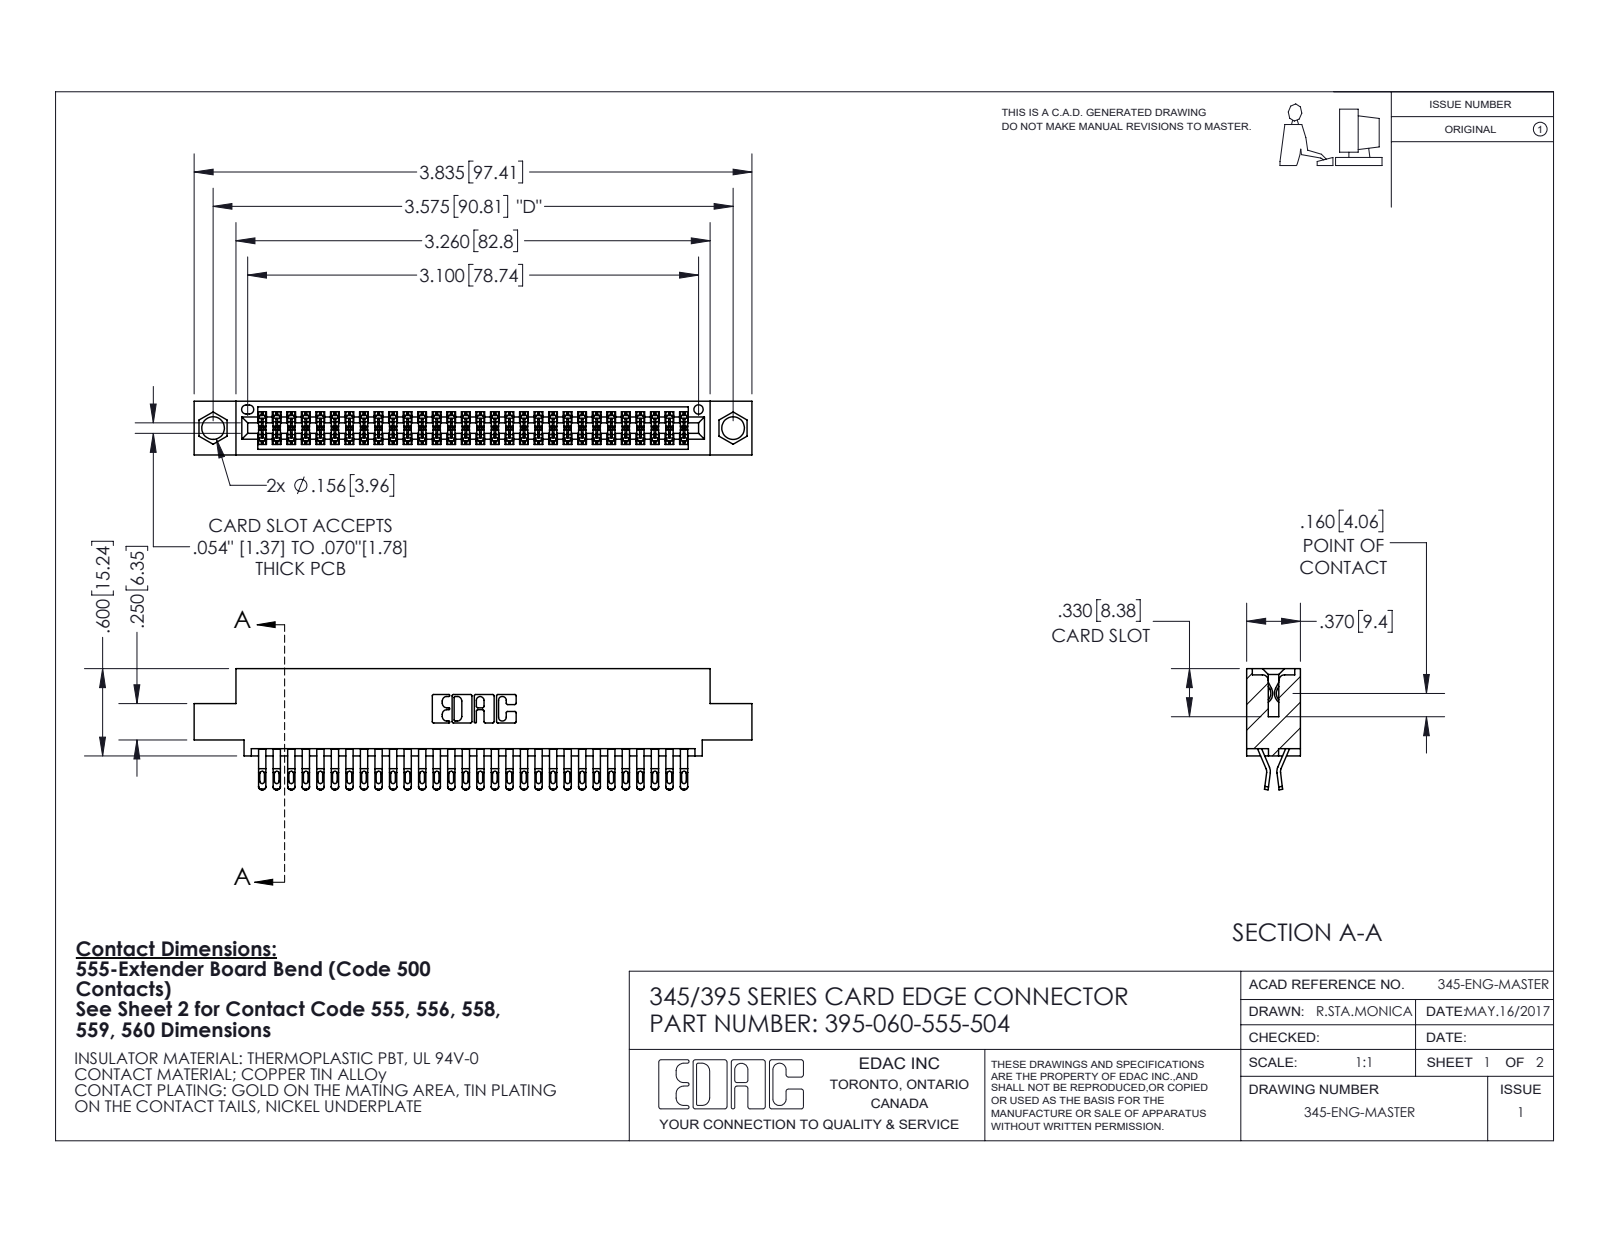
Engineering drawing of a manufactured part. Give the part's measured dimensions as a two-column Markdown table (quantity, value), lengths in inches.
| quantity | value |
| --- | --- |
| part name | 395-060-555-504; 345-292-001_555 Tail; 345 Part_0.110 Offset - 0.156 Dia-TI |
| STEP written by | SolidWorks 2020 (CONFIG_CONTROL_DESIGN) |
| units | inches |
| bodies | 61 solids, 3504 faces (1958 planar, 1546 cylindrical, 0 other) |
| overall size | 3.835 × 0.832 × 0.37 |
| volume | 0.57 in³ |
| surface area | 21.9 in² |
| round holes (diameter × count) | 0.156 × 2, 0.064 × 1 |
| partial cylindrical surfaces (radius × count) | 0.016 × 150, 0.02 × 120, 0.006 × 90, 0.01 × 22, 0.007 × 6, 0.031 × 6, 0.026 × 3, 0.01 × 2 |
| main face-to-face distances | 0.298, 0.072, 0.37, 0.025, 0.2, 0.098, 0.272, 0.225, 0.175, 0.149 |
| hole center spacings | 0.27, 3.34, 3.575 |
